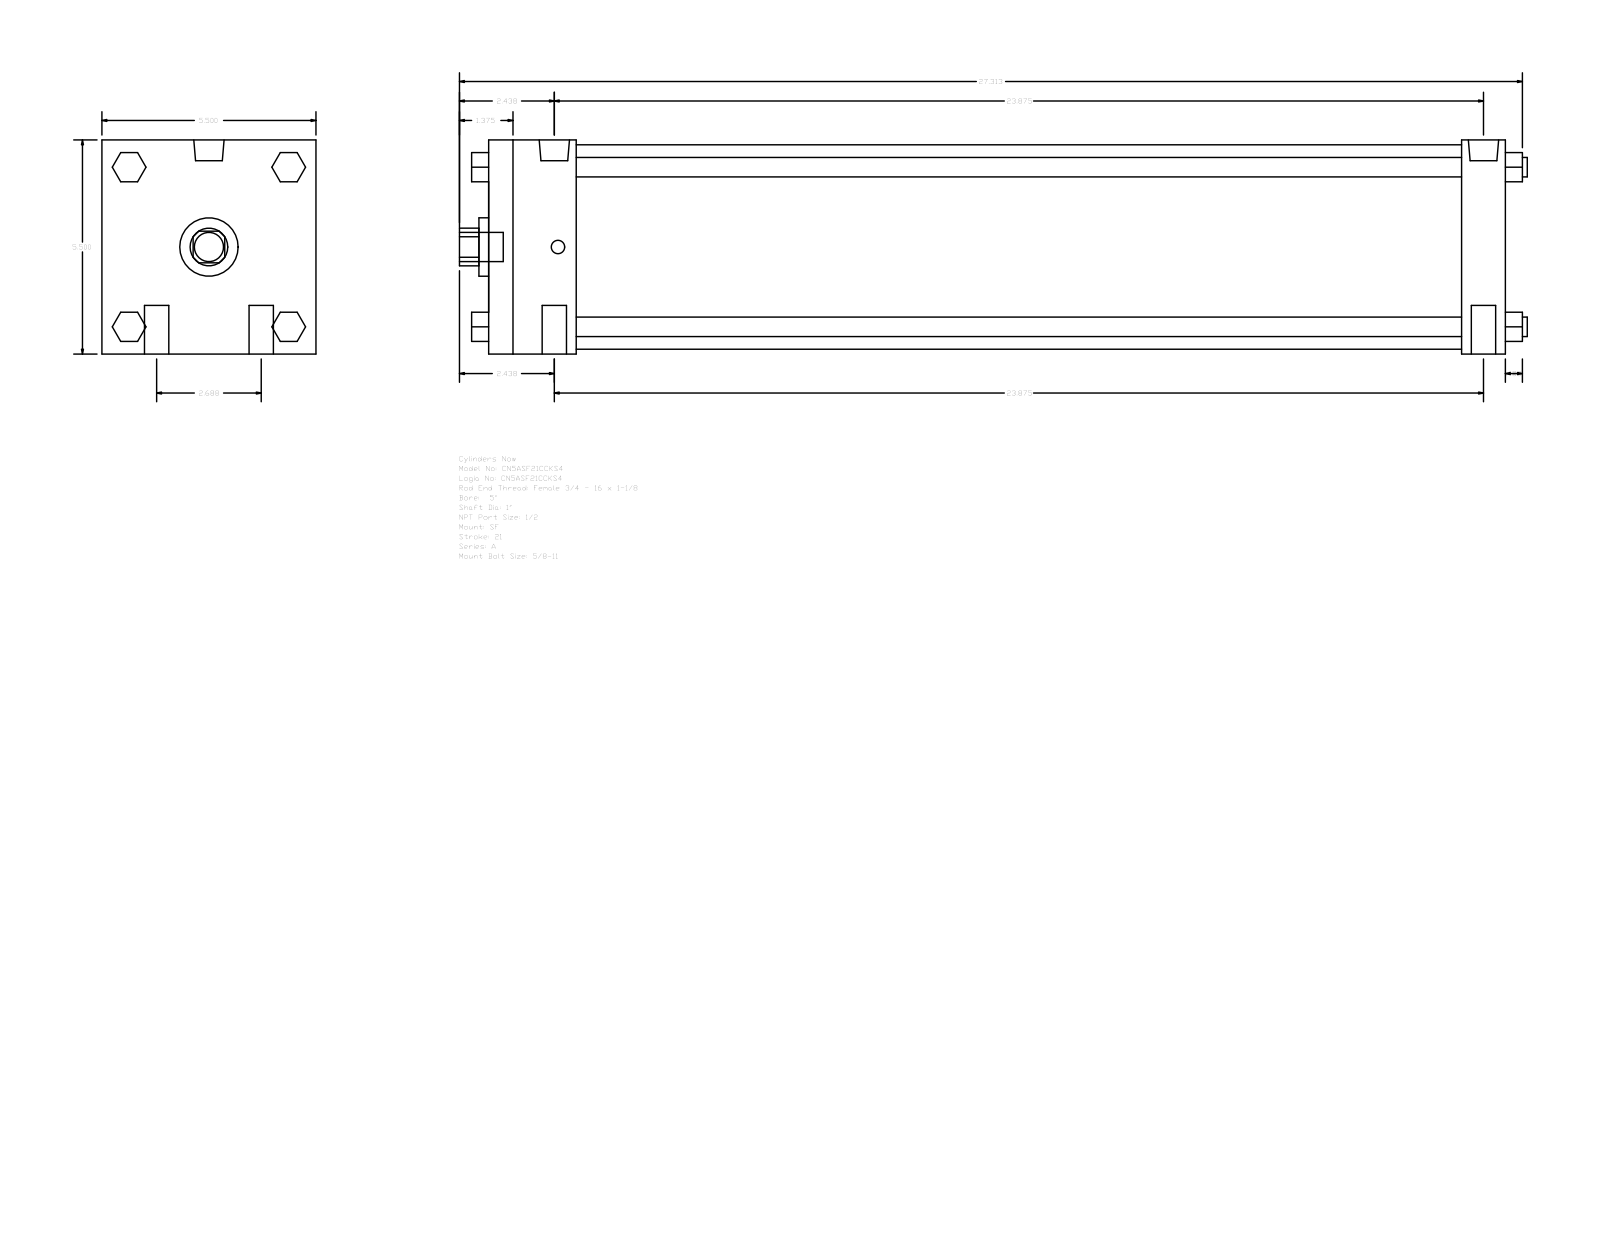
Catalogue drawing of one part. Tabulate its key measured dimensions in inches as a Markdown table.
| quantity | value |
| --- | --- |
| part name | A_SF__0500_1 |
| STEP written by | GSSL Pune (CONFIG_CONTROL_DESIGN) |
| units | inches |
| bodies | 0 solids, 124 faces (94 planar, 30 cylindrical, 0 other) |
| overall size | 27.437 × 5.5 × 5.5 |
| round holes (diameter × count) | 1 × 1, 1.5 × 1, 5.25 × 1 |
| round bosses / shafts (diameter × count) | 0.625 × 4, 0.5 × 4, 0.778 × 2, 0.344 × 2, 0.75 × 1 |
| partial cylindrical surfaces (radius × count) | 0.484 × 1 |
| main face-to-face distances | 5.5, 26.125, 1.125, 2.25, 25, 22.75, 23.875, 0.75, 2.05, 3.55 |
